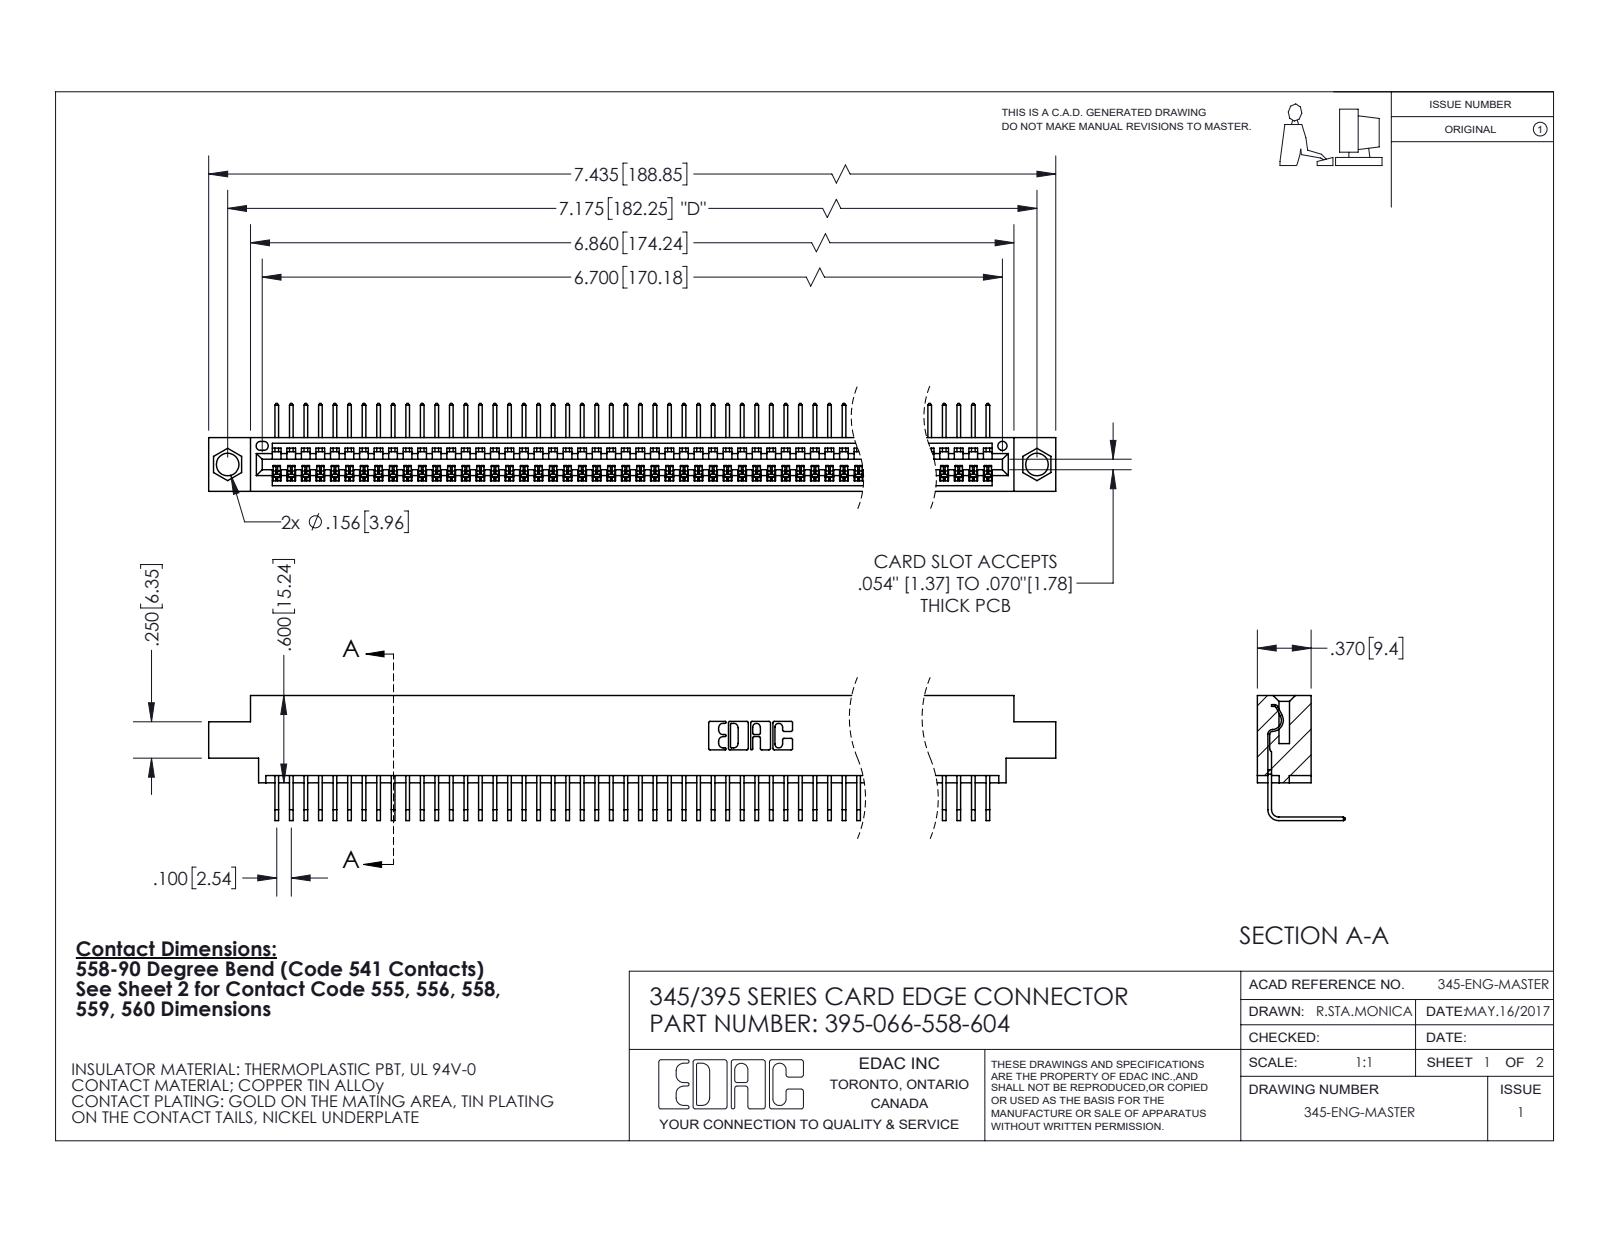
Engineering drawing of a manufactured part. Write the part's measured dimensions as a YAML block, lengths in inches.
part_name: "395-066-558-604; 345-292-001_558 Tail - 2; 345 Part_0.170 Offset - 0.156 Dia-TI"
step_written_by: "SolidWorks 2020 (CONFIG_CONTROL_DESIGN)"
units: inches
bodies: {solids: 67, faces: 4104, planar: 2870, cylindrical: 1234, other: 0}
overall_size: [7.435, 0.859, 0.605]
volume: 1.107
surface_area: 39.81
round_holes:
  - {diameter: 0.156, count: 2}
  - {diameter: 0.064, count: 1}
partial_cylinders:
  - {radius: 0.006, count: 132}
  - {radius: 0.01, count: 22}
  - {radius: 0.007, count: 6}
  - {radius: 0.031, count: 6}
  - {radius: 0.026, count: 3}
  - {radius: 0.031, count: 2}
  - {radius: 0.04, count: 2}
  - {radius: 0.014, count: 1}
face_to_face_distances: [0.072, 0.298, 0.37, 0.2, 0.098, 0.272, 0.025, 0.225, 0.175, 0.149]
hole_center_spacings: [0.27, 6.939, 7.175]
